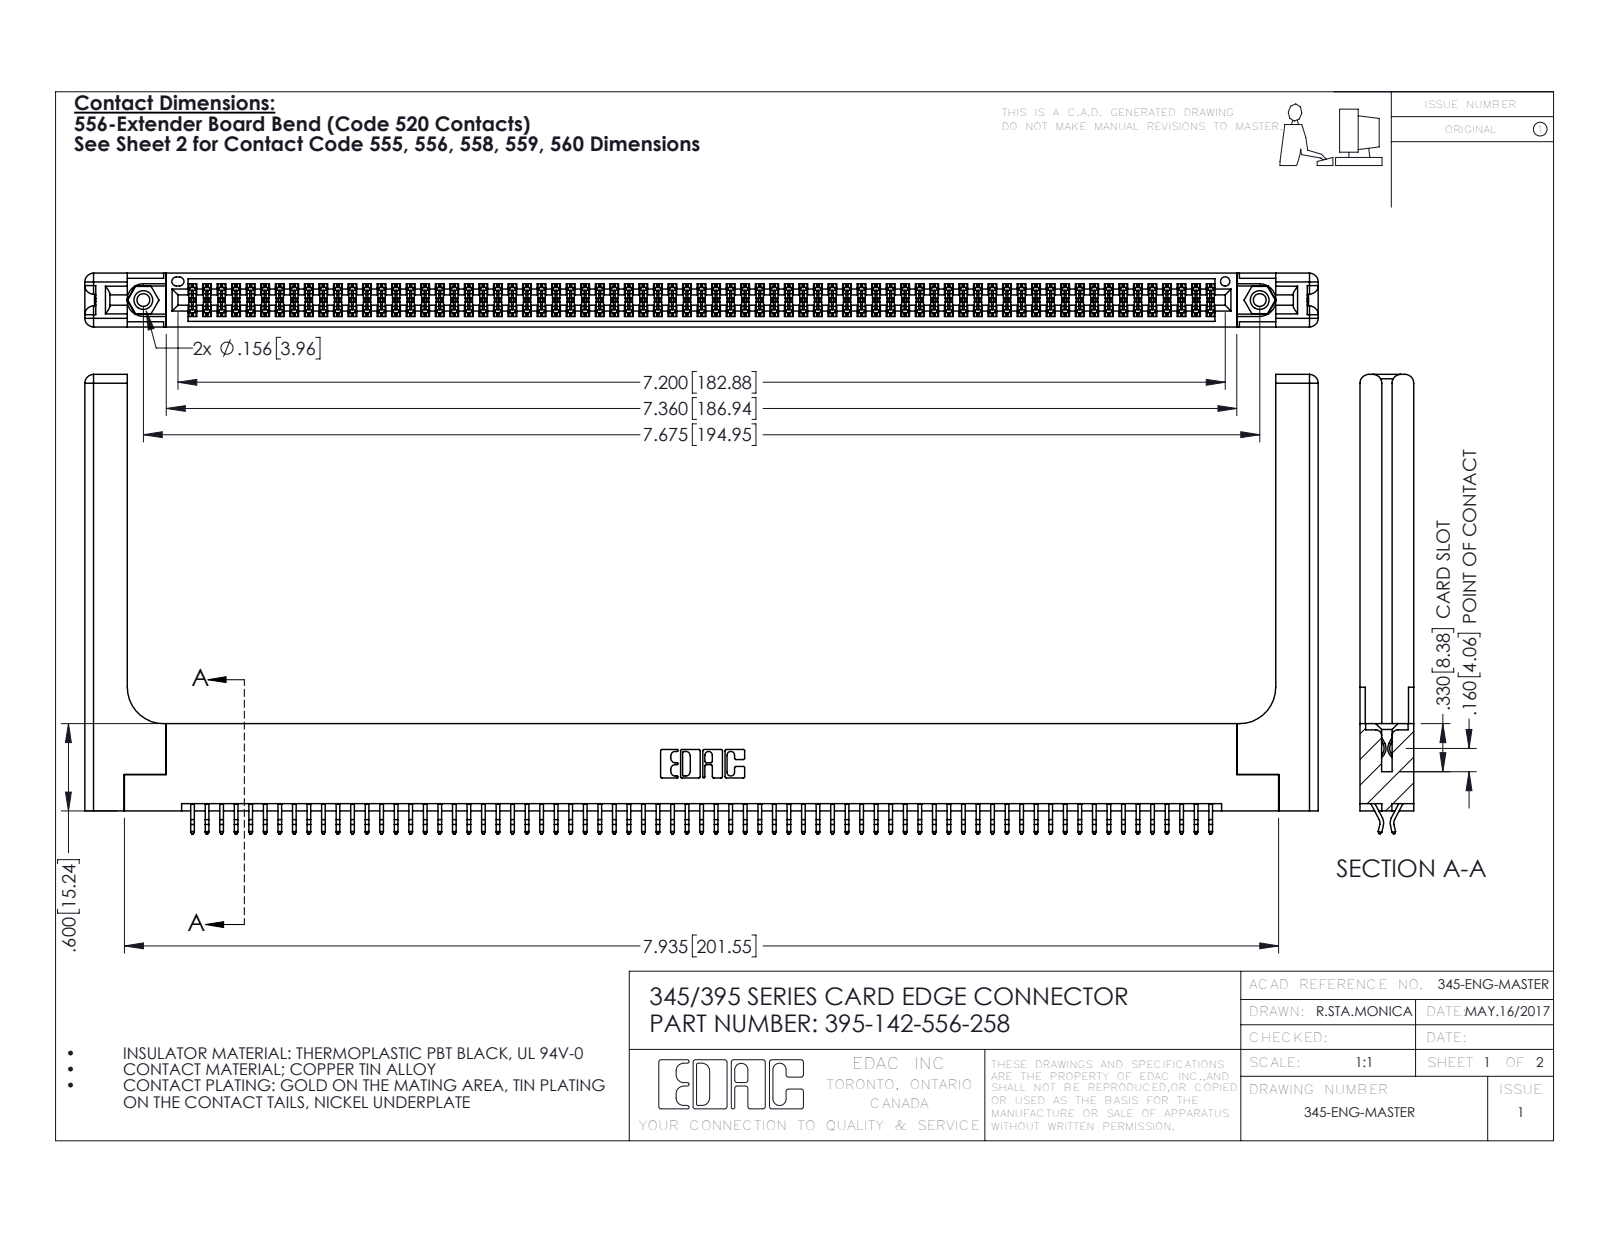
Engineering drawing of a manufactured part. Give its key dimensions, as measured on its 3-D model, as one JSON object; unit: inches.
{"part_name": "345-292-001_556 Tail; 345-220-058_345-220-058; 345 Part_Flush Mounting Lugs - 0.156 Dia-TH; 395-142-556-258 (+1 more)", "step_written_by": "SolidWorks 2016 (CONFIG_CONTROL_DESIGN)", "units": "inches", "bodies": {"solids": 147, "faces": 8334, "planar": 5482, "cylindrical": 2792, "other": 60}, "overall_size": [8.479, 3.157, 0.37], "volume_in3": 1.81, "surface_area_in2": 57.06, "round_holes": [[0.089, 2], [0.125, 2], [0.156, 2], [0.064, 1]], "round_bosses_or_shafts": [[0.155, 2]], "partial_cylinders_radius": [[0.006, 213], [0.01, 22], [0.06, 16], [0.007, 6], [0.031, 6], [0.026, 3], [0.01, 2], [0.014, 2]], "face_to_face_distances": [0.072, 0.298, 0.37, 0.2, 0.025, 0.098, 0.272, 0.225, 0.175, 0.148], "hole_center_spacings": [0.27, 7.439, 7.675]}
